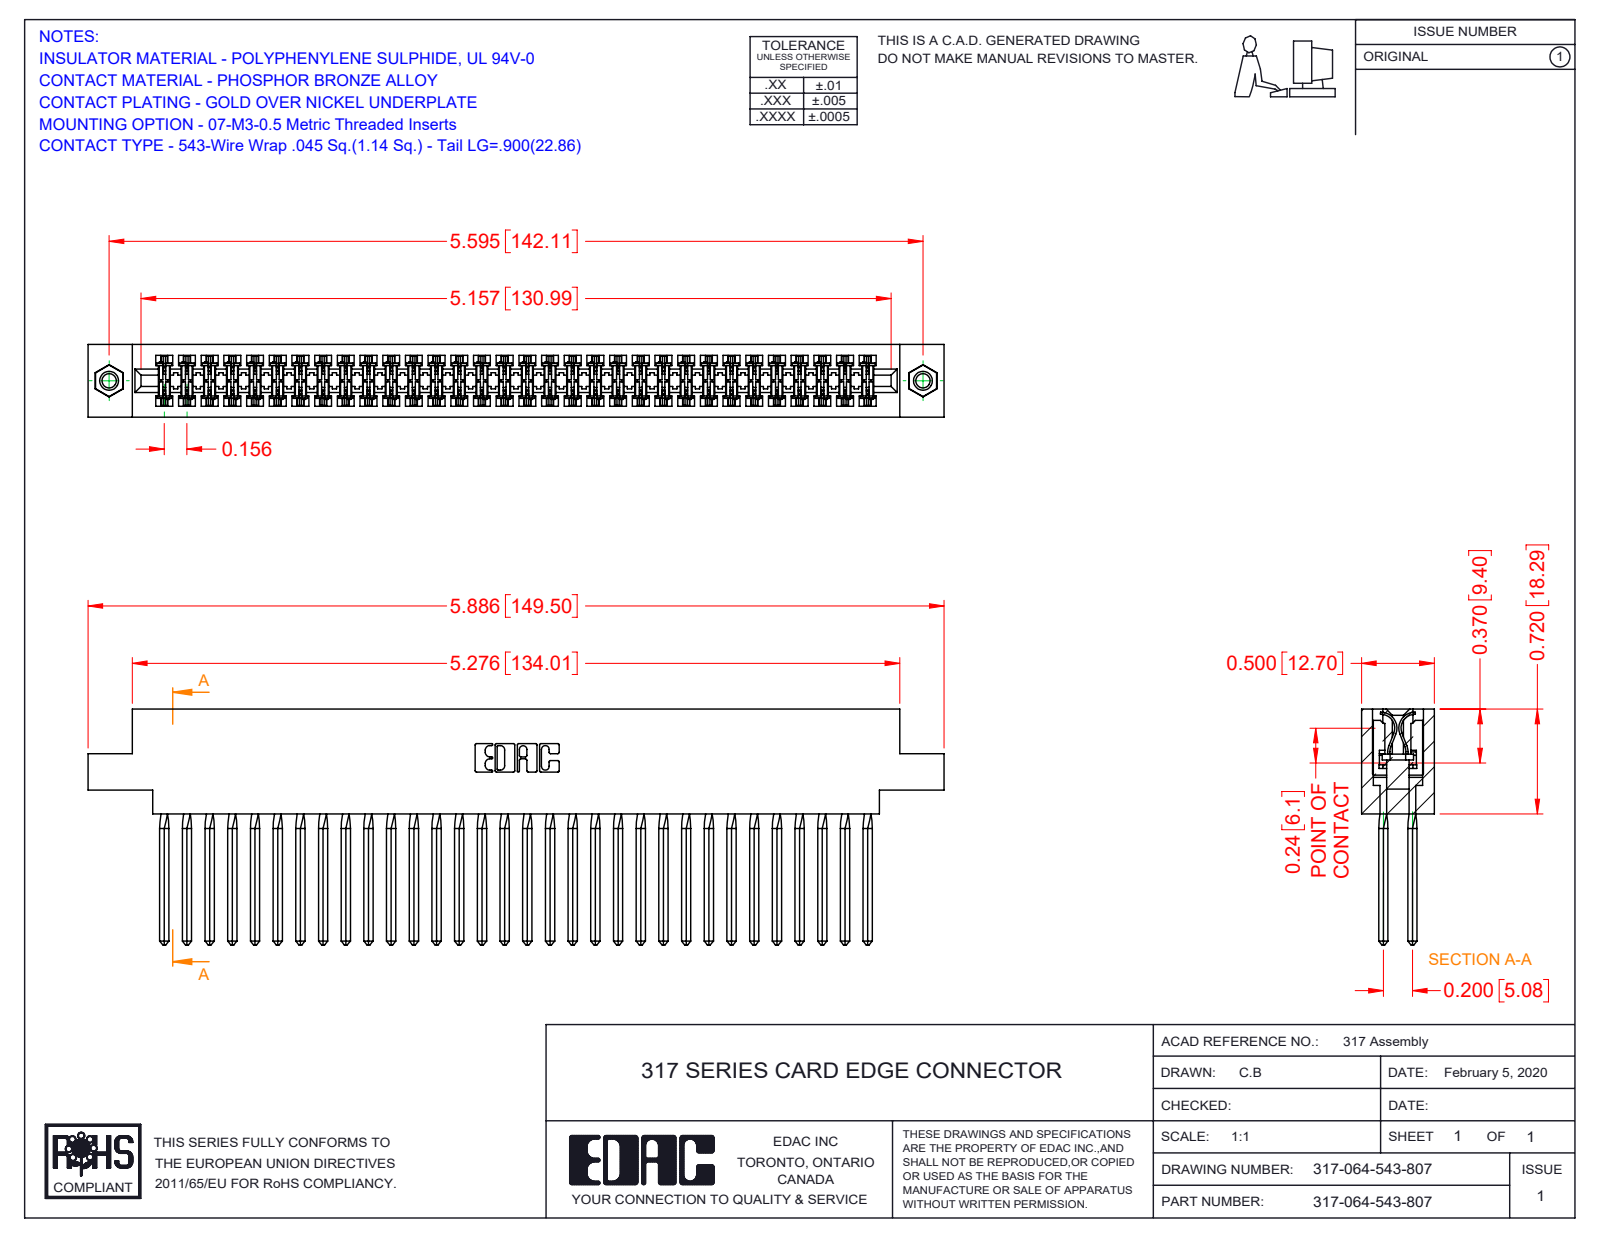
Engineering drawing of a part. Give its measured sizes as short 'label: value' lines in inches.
name: 317-290-001_543; 317-064-543-807; 345-250-001_345-250-005-103; 317 Part_.156 Dia - TI
written by: SolidWorks 2016 (CONFIG_CONTROL_DESIGN)
unit: in
bodies: 67 solids, 5858 faces (4762 planar, 824 cylindrical, 272 other)
size: 5.886 × 1.62 × 0.5
volume: 1.529 in³; area: 58.37 in²
holes: 2× ⌀0.098, 2× ⌀0.125, 2× ⌀0.156
bosses: 2× ⌀0.155
rounds: 128× R0.015, 22× R0.01, 6× R0.007, 6× R0.031, 3× R0.026, 2× R0.095, 2× R0.1, 2× R0.11
face distances: 0.5, 0.075, 0.425, 0.35, 0.11, 0.195, 0.094, 0.2, 0.115, 0.131
hole spacings: 5.595
